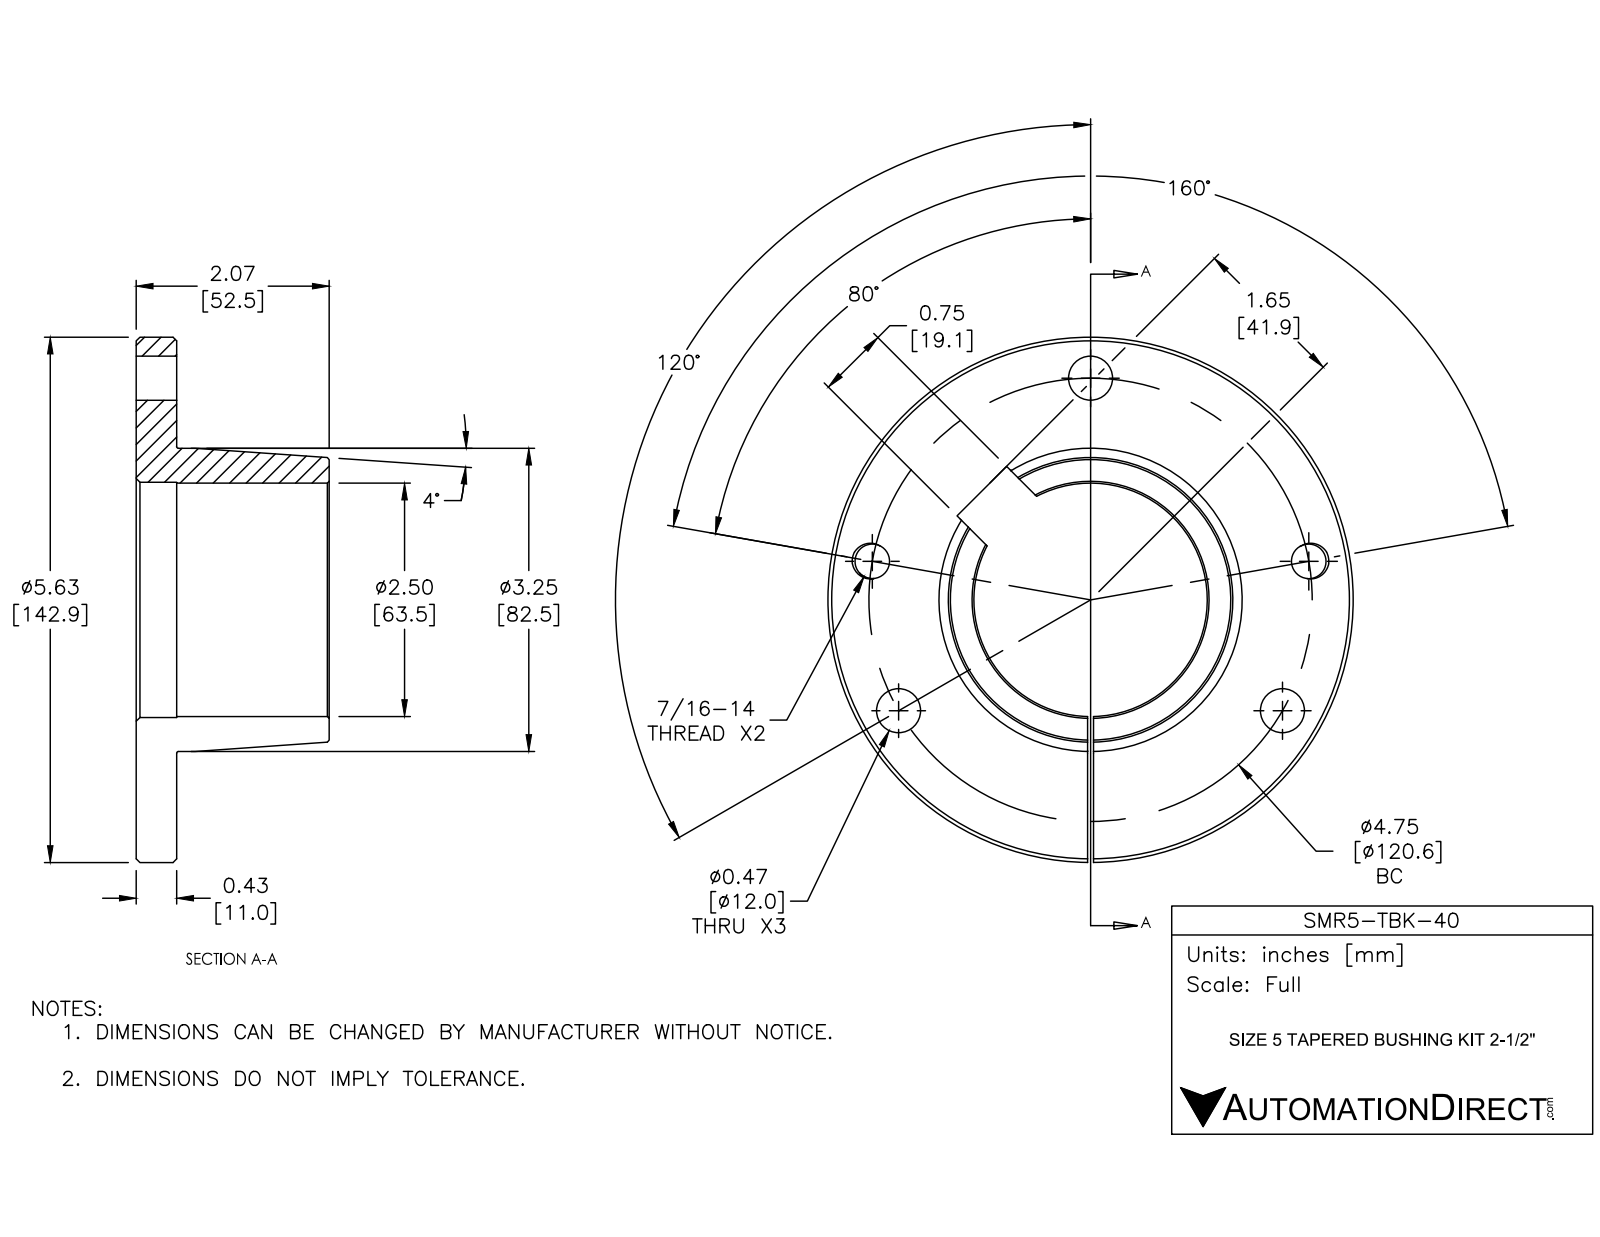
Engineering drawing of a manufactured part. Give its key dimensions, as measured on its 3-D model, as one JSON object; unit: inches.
{"part_name": "SMR5-TBK-40", "step_written_by": "SolidWorks 2016 (AUTOMOTIVE_DESIGN)", "units": "inches", "bodies": {"solids": 1, "faces": 98, "planar": 11, "cylindrical": 67, "other": 20}, "overall_size": [5.626, 5.626, 2.067], "volume_in3": 12.41, "surface_area_in2": 80.25, "round_holes": [[0.472, 3], [0.37, 2], [0.43, 2], [2.5, 1], [2.52, 1]], "round_bosses_or_shafts": [[5.626, 1], [3.247, 1]], "face_to_face_distances": [0.433, 2.067, 1.634, 0.063, 0.75], "hole_center_spacings": [2.374, 4.112, 4.676, 1.624, 3.052]}
